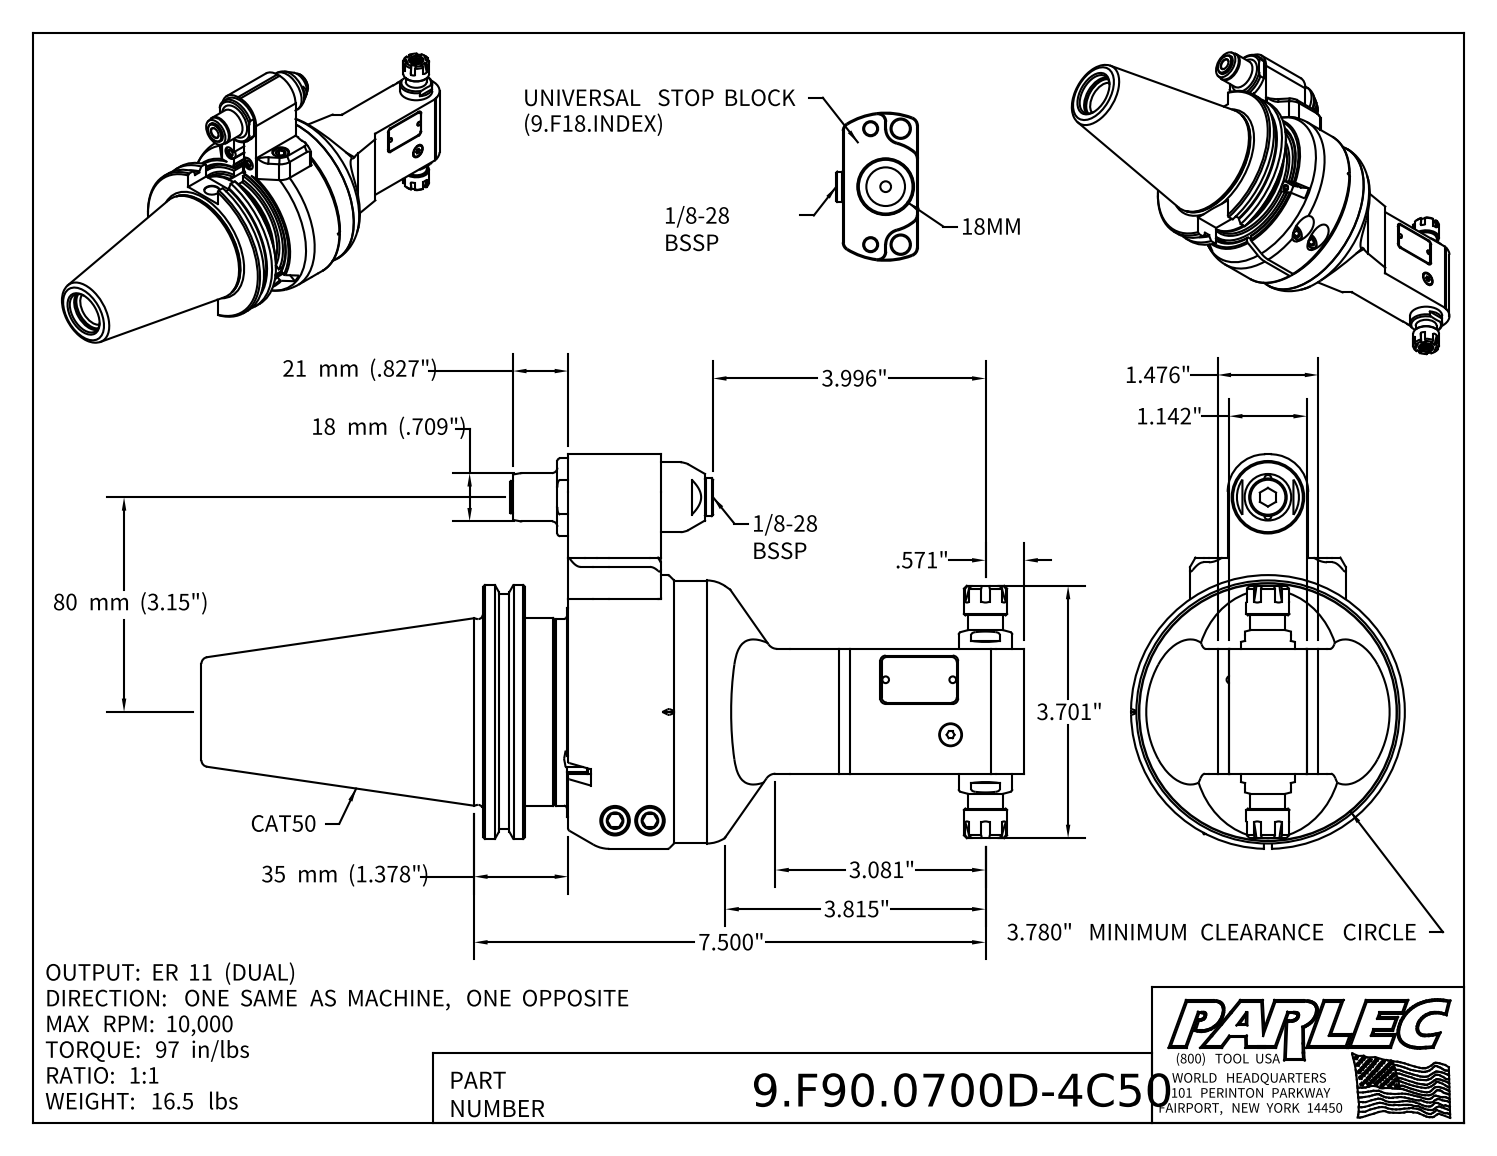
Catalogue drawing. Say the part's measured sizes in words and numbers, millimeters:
The part is named "9.F90.0700D-4C50; 9_F90_07000_2U; 9GA11C_458". Its 3-D file was written by "Autodesk Inventor 2025 (AUTOMOTIVE_DESIGN)". It is 4 solids with 637 faces: 295 planar, 183 cylindrical and 159 other. Overall it measures 306.6 by 147 by 102 millimeters. Its volume is 1 087 000 cubic millimeters and its surface area 164 200 square millimeters. Round holes: 21 of diameter 8.5, 3 of diameter 6.5, 2 of diameter 2.6, 2 of diameter 3.3, 2 of diameter 4.2, 2 of diameter 5, 2 of diameter 8, 2 of diameter 10.4, 2 of diameter 10.5, 2 of diameter 11, 2 of diameter 12.5, 1 of diameter 2.5. Round bosses or shafts: 4 of diameter 10, 2 of diameter 18, 2 of diameter 12, 2 of diameter 8, 2 of diameter 6, 2 of diameter 2.5, 1 of diameter 102, 1 of diameter 98.4. Partial cylindrical surfaces (rounded edges, fillets, slot ends): 14 of radius 1, 12 of radius 2, 12 of radius 30, 6 of radius 3, 4 of radius 4, 2 of radius 0.5, 2 of radius 8, 2 of radius 14. The main face-to-face distances are 0.5, 32.5, 32, 55.4, 23.4, 23, 71.3, 39.3, 38.8, 15.9. The hole center spacings are 38.5, 46.3, 54.4, 76.3, 10.7, 61.5, 21.2, 31.3.
